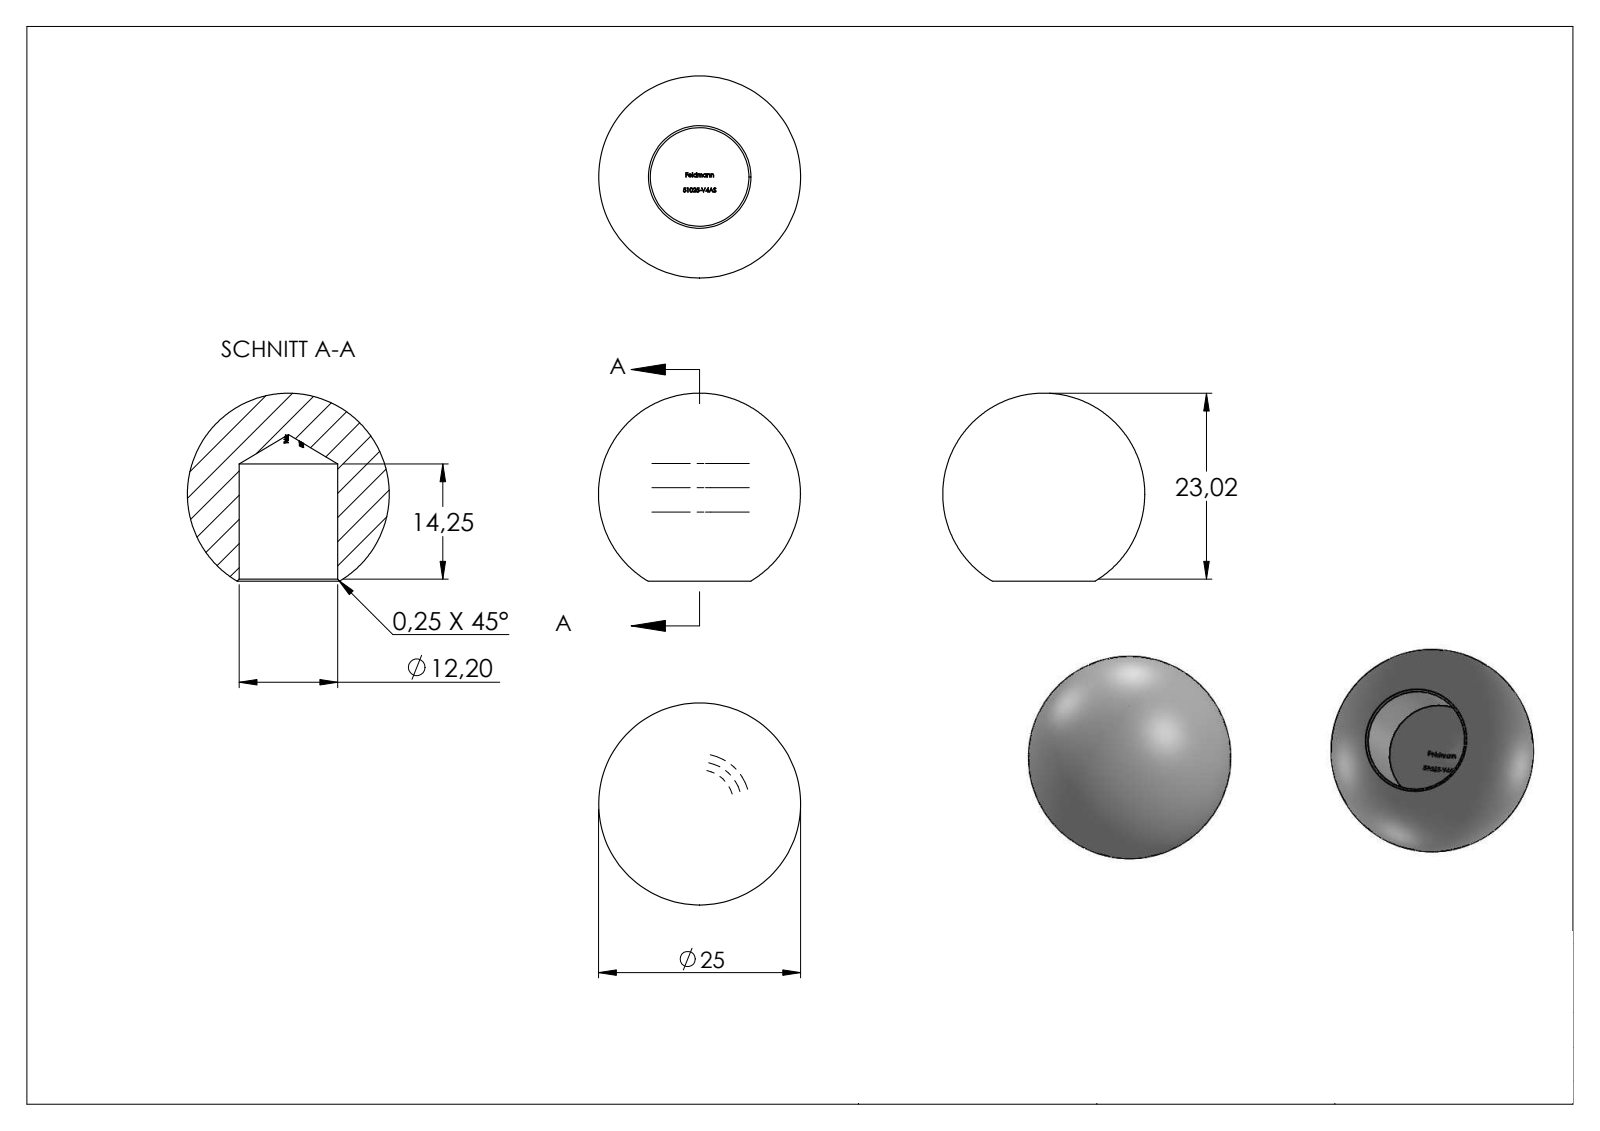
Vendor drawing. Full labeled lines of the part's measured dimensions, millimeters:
Part name (STEP PRODUCT): 51025-V4AS
STEP written by: SolidWorks 2015 (CONFIG_CONTROL_DESIGN)
Units: millimetres
Bodies: 1 solid, 248 faces (115 planar, 2 cylindrical, 131 other)
Overall size (bounding box): 25 × 25 × 23.27
Volume: 6 230 mm³ · Surface area: 2 528 mm²
Round holes (diameter × count): ⌀12.2 ×1
Main face-to-face distances: 1.19, 0.56, 1.88, 1.35, 0.53, 1.75, 1.31, 0.61, 0.66, 0.35
